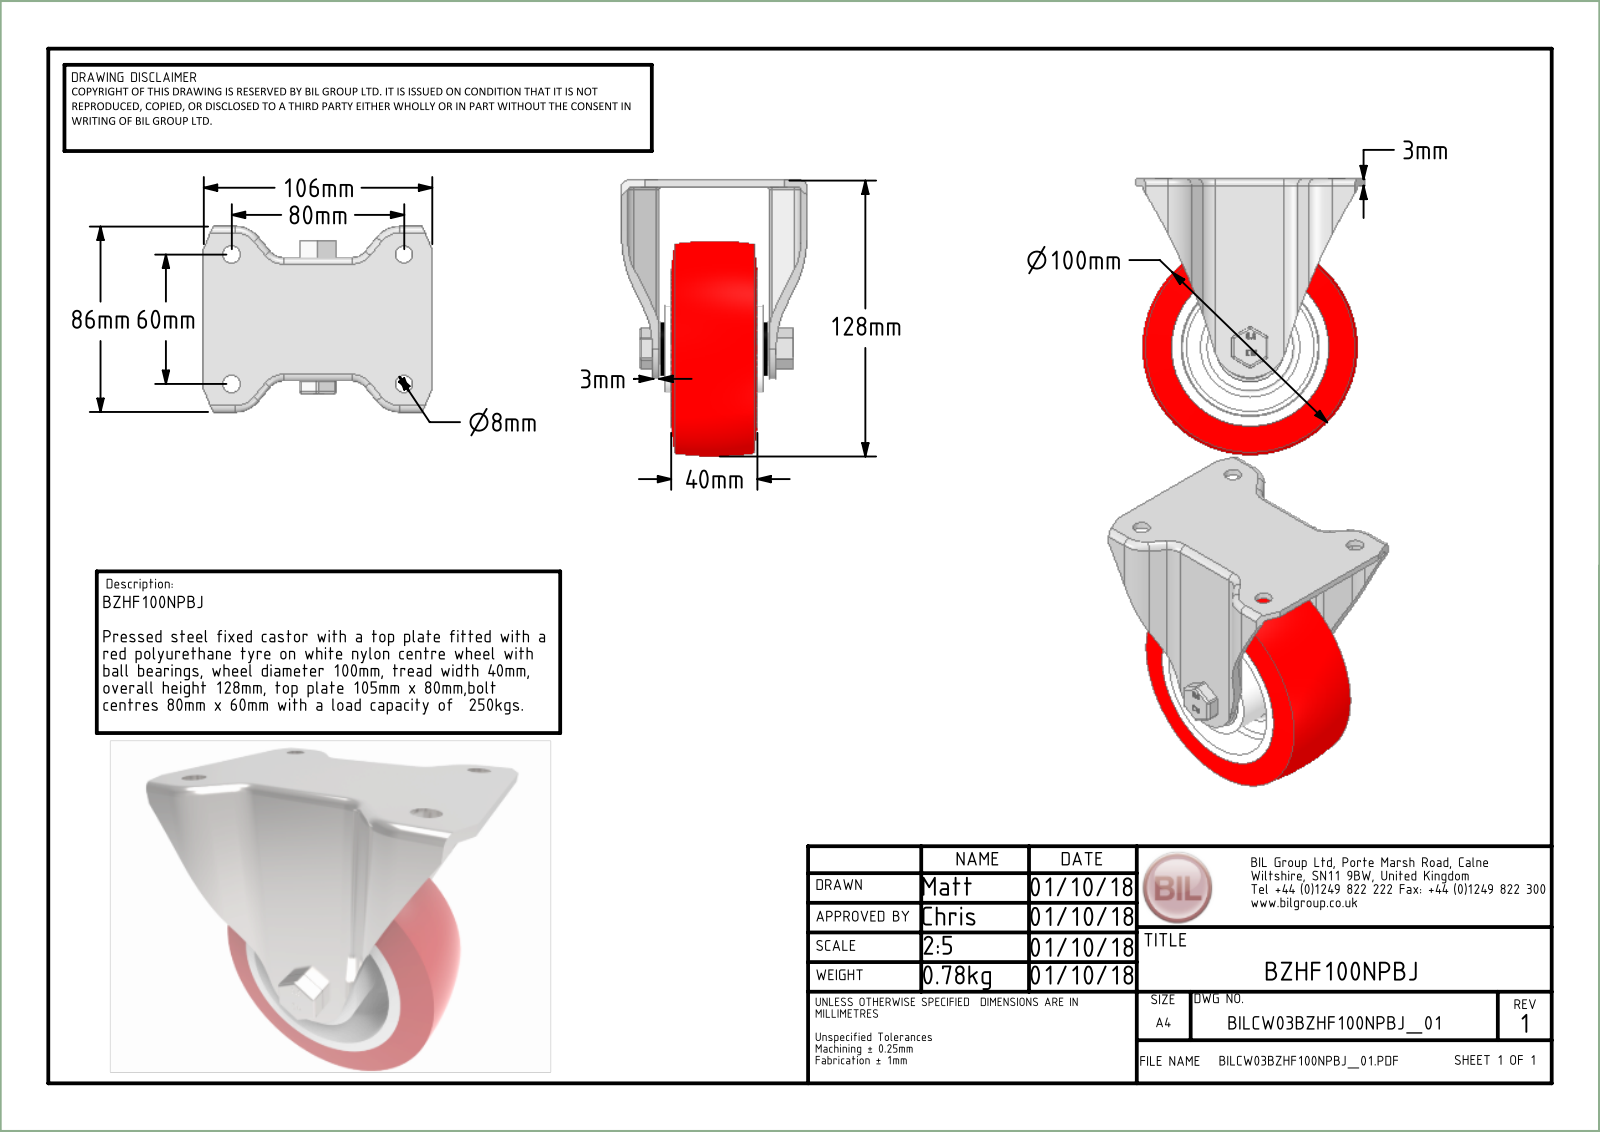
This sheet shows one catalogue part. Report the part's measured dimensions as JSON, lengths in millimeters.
{"part_name": "BZHF100NPBJ v3; BZHF100AS - 52 v1; ZINC PLATED, PRESSED STEEL BRACKET; BZH100WNPBJM15 v1 (+7 more)", "step_written_by": "Autodesk Translation Framework v14.10.0.0 (AUTOMOTIVE_DESIGN)", "units": "millimeters", "bodies": {"solids": 38, "faces": 1123, "planar": 388, "cylindrical": 209, "other": 526}, "overall_size": [128, 106, 88], "volume_mm3": 298660, "surface_area_mm2": 127030, "round_holes": [[10, 1], [10.25, 1], [10.5, 1], [12, 1], [15, 1], [15.75, 1], [20.5, 1], [26.8, 1], [28, 1], [28.2, 1], [30, 1], [32, 1]], "round_bosses_or_shafts": [[40, 1], [25, 1], [21.5, 1], [20, 1], [19, 1], [16, 1], [9.85, 1], [8.14, 1]], "partial_cylinders_radius": [[0.5, 18], [1.5, 12], [3, 10], [4.5, 8], [0.75, 6], [6, 4], [8, 4], [12, 4]], "face_to_face_distances": [3, 6, 46, 26.5, 9, 5, 40, 49, 55, 17.5]}
